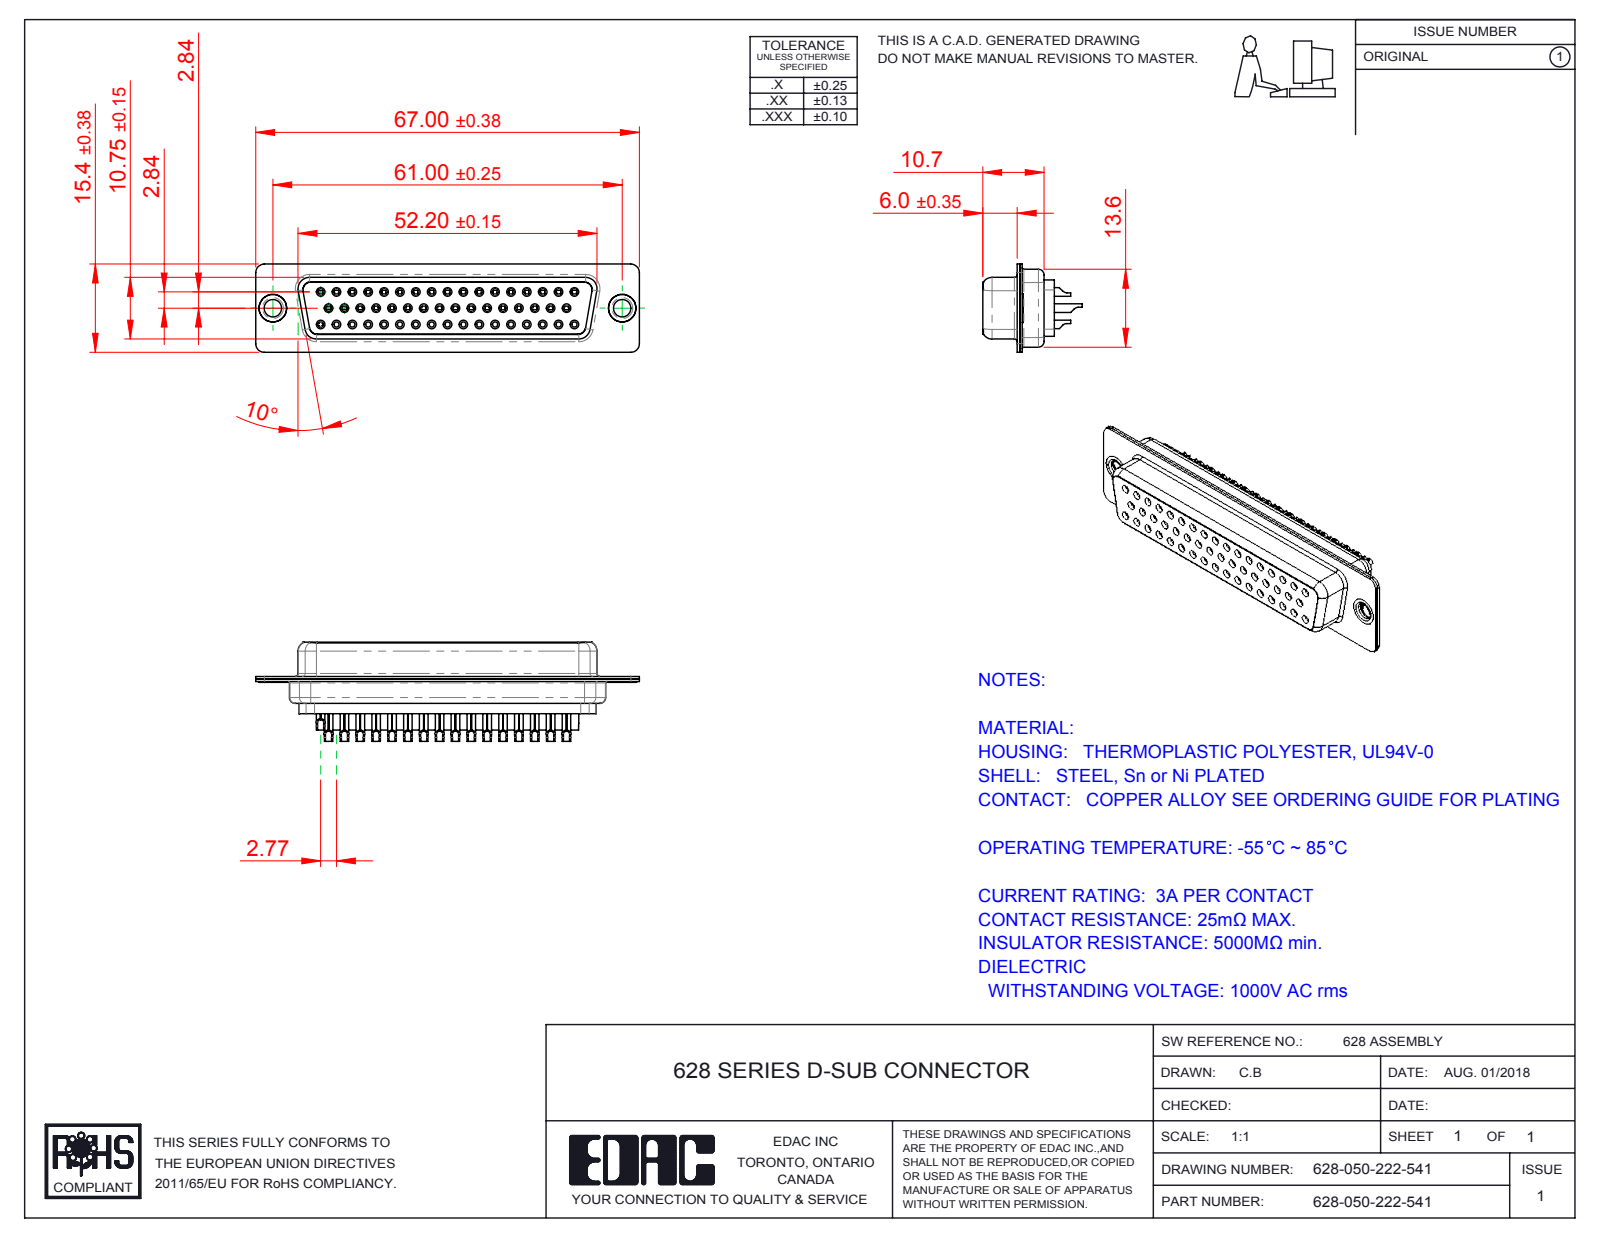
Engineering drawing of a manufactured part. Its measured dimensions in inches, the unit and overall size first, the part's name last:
Units: inches
Overall size (bounding box): 2.638 × 0.683 × 0.606
Round holes (diameter × count): ⌀0.035 ×50, ⌀0.063 ×50, ⌀0.031 ×34, ⌀0.043 ×34, ⌀0.067 ×17, ⌀0.059 ×16, ⌀0.079 ×16, ⌀0.12 ×2, ⌀0.157 ×2, ⌀0.189 ×2
Round bosses / shafts (diameter × count): ⌀0.079 ×34, ⌀0.059 ×34, ⌀0.047 ×34, ⌀0.197 ×2, ⌀0.193 ×2, ⌀0.14 ×2
Partial cylindrical surfaces — rounded edges, fillets, slot ends (radius × count): R0.011 ×33, R0.059 ×16, R0.079 ×12, R0.053 ×8, R0.039 ×7, R0.01 ×4, R0.02 ×4, R0.024 ×4
Main face-to-face distances: 0.018, 0.016, 0.406, 0.238, 0.035, 0.256, 0.492, 0.254, 0.236, 0.446
Hole centre spacings: 0.124, 0.109, 0.218, 0.327, 0.436, 0.545, 0.654, 0.763
Volume: 0.4 in³ · Surface area: 21.67 in²
Bodies: 39 solids, 3487 faces (829 planar, 1099 cylindrical, 1559 other)
Part name (STEP PRODUCT): 628 Housing_50 LP; 628 Thru Hole Rivet; 628 Contact Row 2_22M; 628 Contact Row 3_22L (+4 more)
STEP written by: SolidWorks 2016 (CONFIG_CONTROL_DESIGN)
